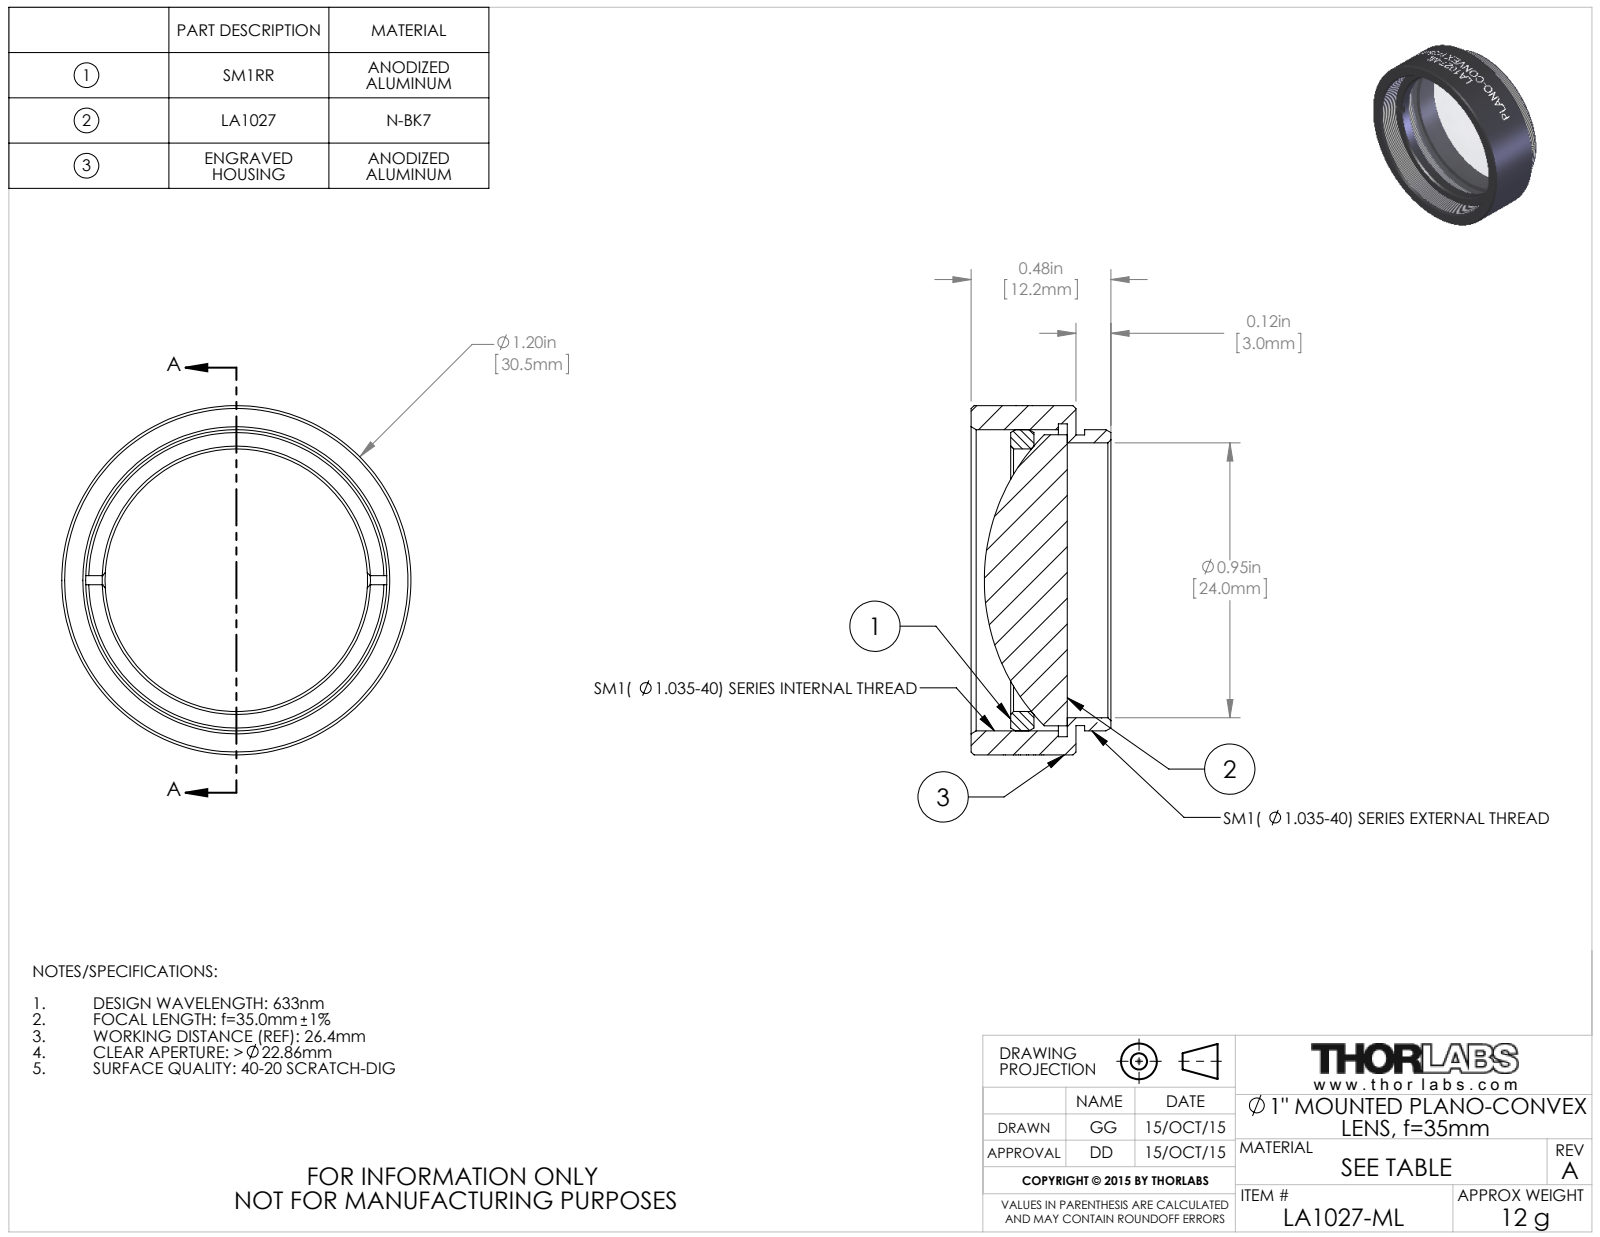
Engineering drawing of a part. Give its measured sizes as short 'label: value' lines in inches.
name: TTN039471-E0W
written by: SolidWorks 2014 (CONFIG_CONTROL_DESIGN)
unit: in
bodies: 3 solids, 113 faces (20 planar, 69 cylindrical, 24 other)
size: 1.2 × 1.2 × 0.48
volume: 0.283 in³; area: 7.028 in²
holes: 1× ⌀0.902, 1× ⌀0.945, 1× ⌀1.035, 1× ⌀1.075
bosses: 1× ⌀1.2, 1× ⌀1.035, 1× ⌀1, 1× ⌀0.999
face distances: 0.03, 0.36, 0.33, 0.144, 0.115, 0.215, 0.224, 0.194, 0.08, 0.135
